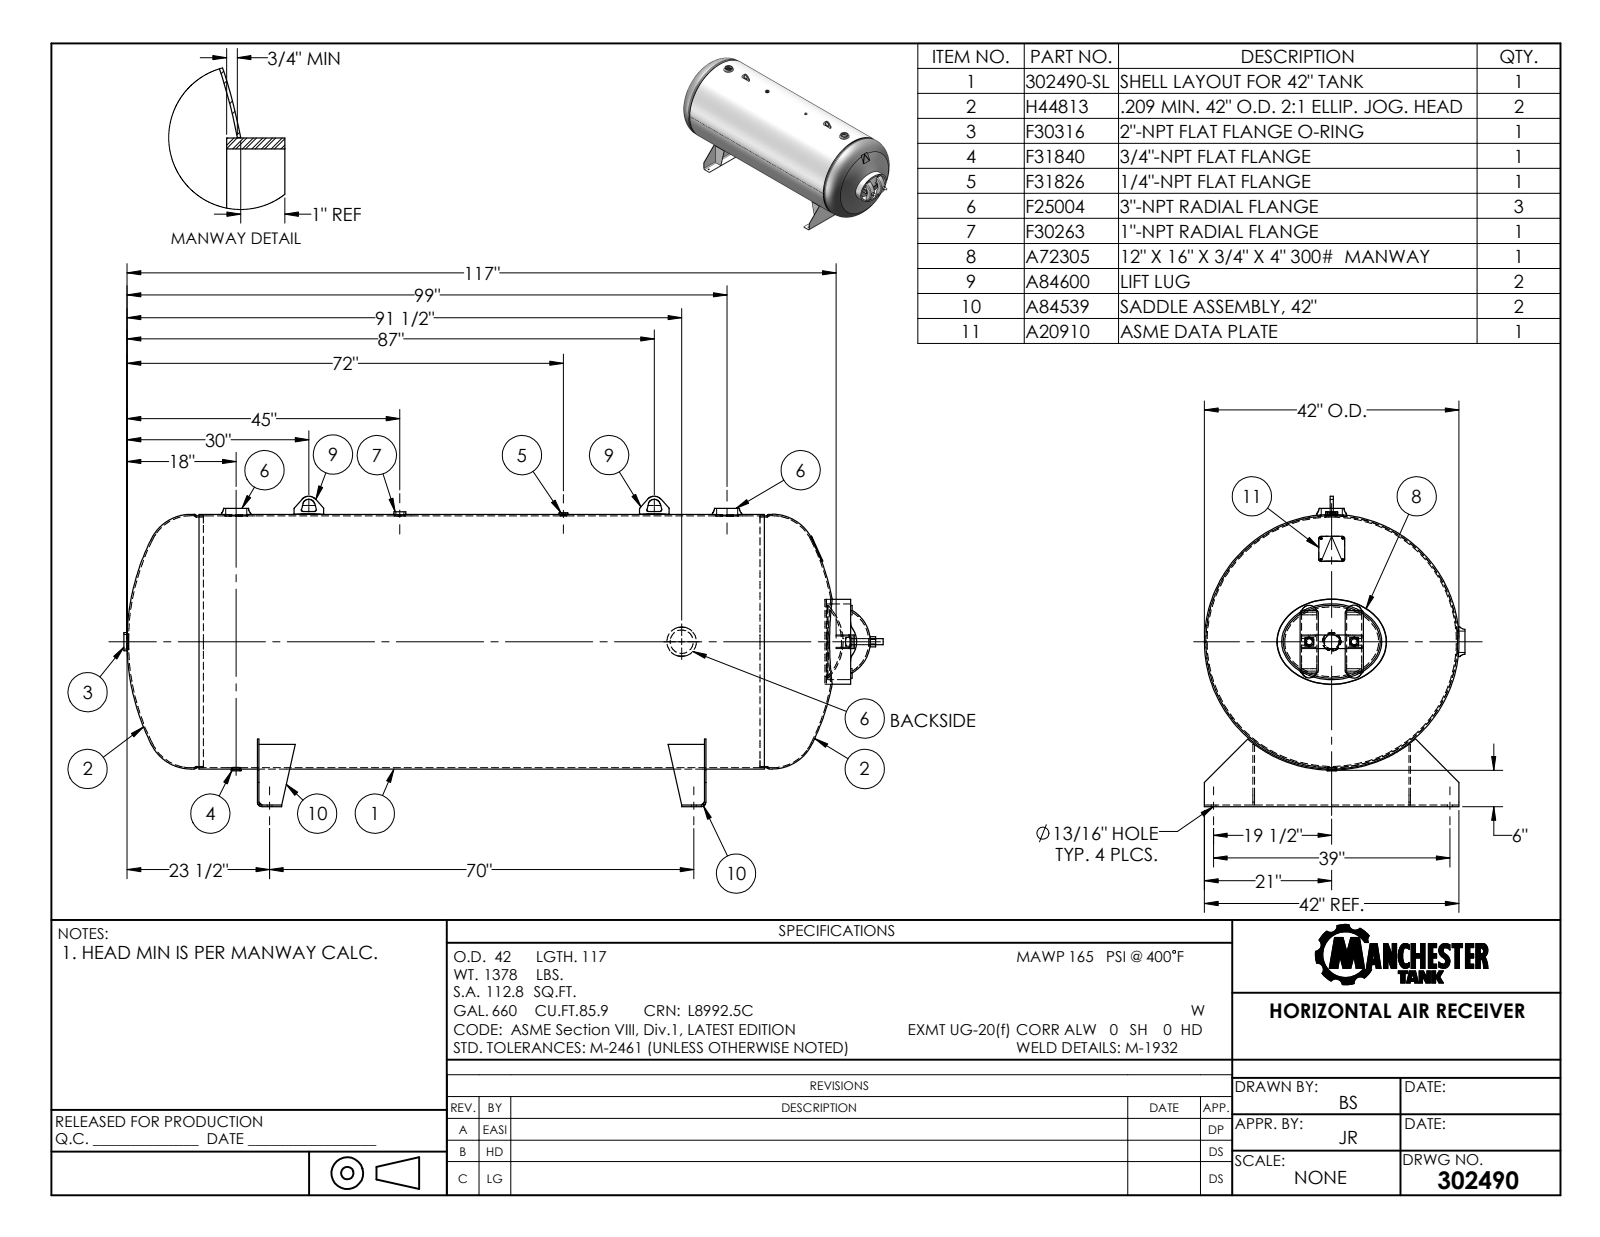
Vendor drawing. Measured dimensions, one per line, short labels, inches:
name: 302490
written by: SolidWorks 2011 (CONFIG_CONTROL_DESIGN)
unit: in
bodies: 0 solids, 281 faces (116 planar, 77 cylindrical, 88 other)
size: 123.371 × 51 × 43.02
holes: 4× ⌀0.813, 3× ⌀3.5, 2× ⌀1.125, 1× ⌀0.54, 1× ⌀1.05, 1× ⌀1.315, 1× ⌀2.375
bosses: 3× ⌀4.875, 2× ⌀1, 1× ⌀42, 1× ⌀41.5, 1× ⌀3.5, 1× ⌀2.875, 1× ⌀2.375, 1× ⌀2.063
rounds: 4× R1.318, 3× R0.375, 2× R0.063, 2× R0.313, 2× R3, 1× R5.917, 1× R6, 1× R27.06
face distances: 0.25, 73.75, 74, 73.5, 25.75, 26, 25.5, 9.625, 9.875, 83.375
hole spacings: 20.261, 29.026, 52.273, 77.978, 27, 39, 54, 70
